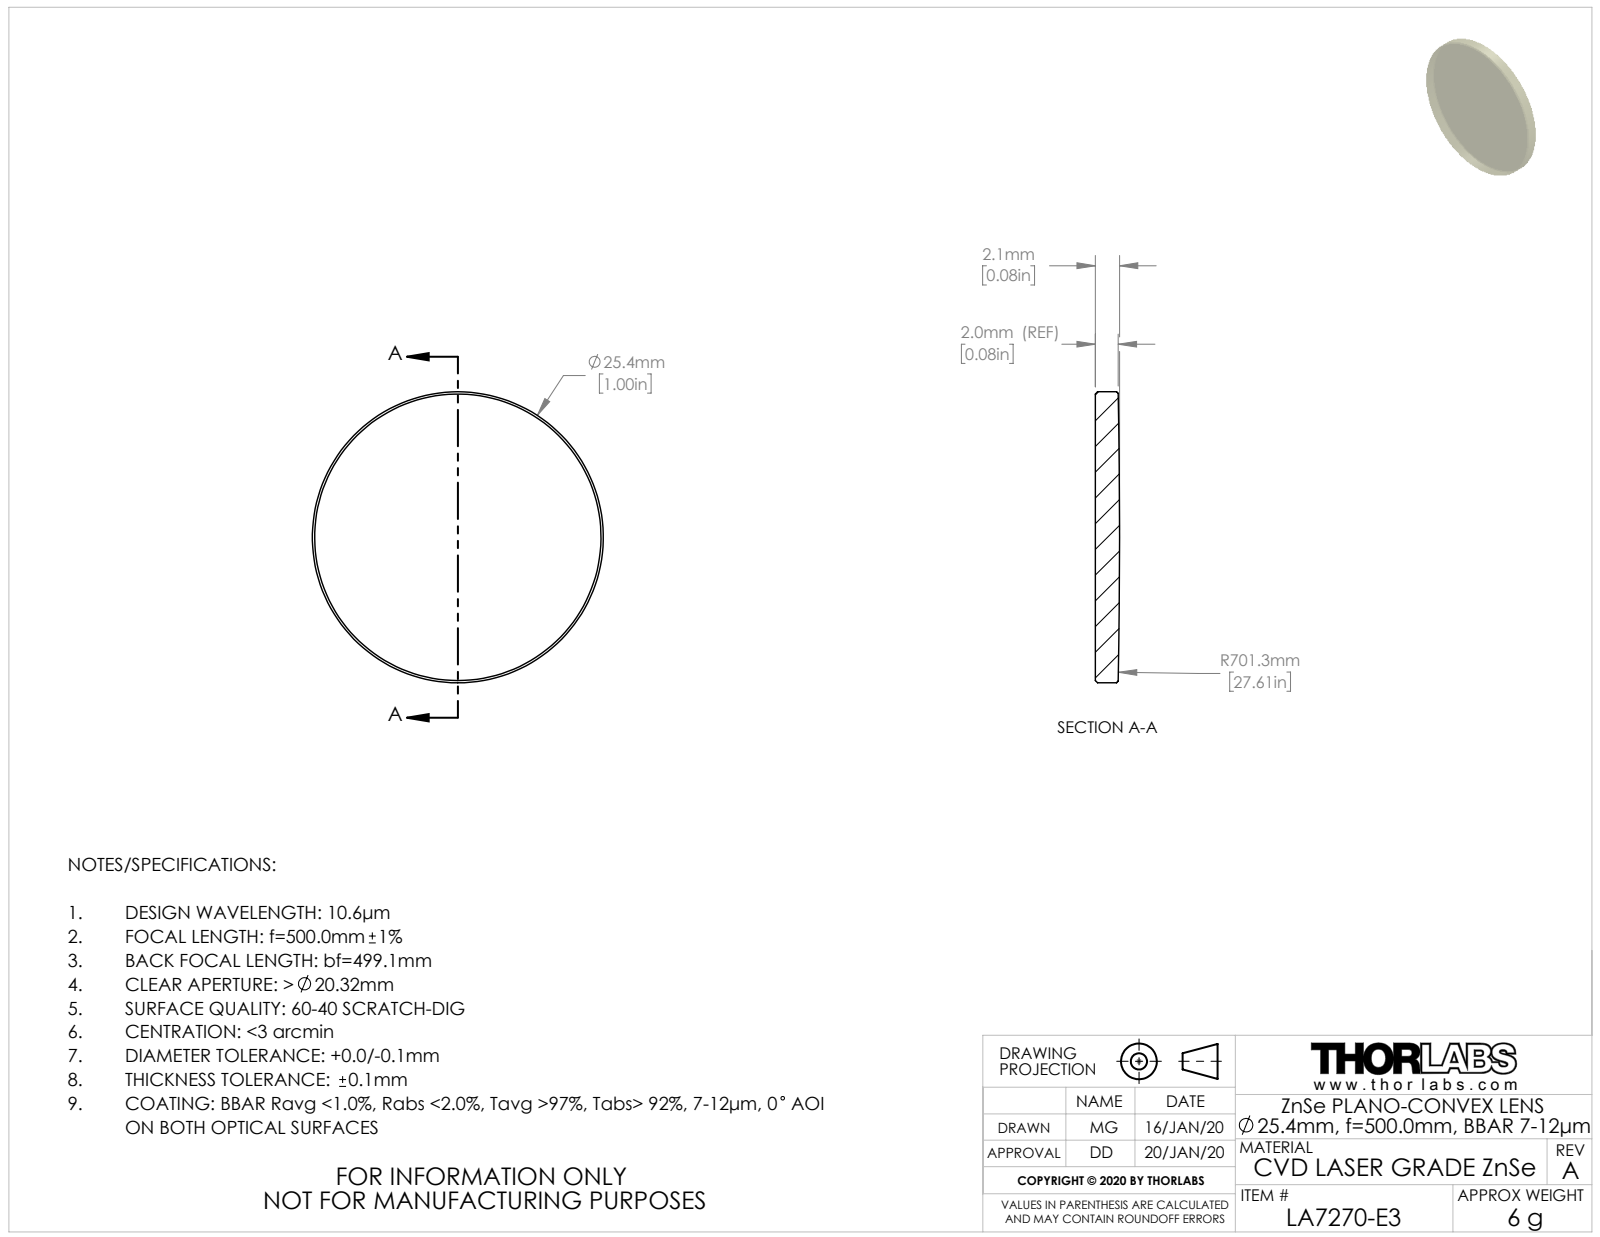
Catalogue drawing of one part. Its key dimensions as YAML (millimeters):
part_name: "TTN206029-E0W"
step_written_by: "SolidWorks 2018 (CONFIG_CONTROL_DESIGN)"
units: millimeters
bodies: {solids: 1, faces: 9, planar: 1, cylindrical: 2, other: 6}
overall_size: [25.4, 25.4, 2.11]
volume: 1038
surface_area: 1157
round_bosses_or_shafts:
  - {diameter: 25.4, count: 1}
